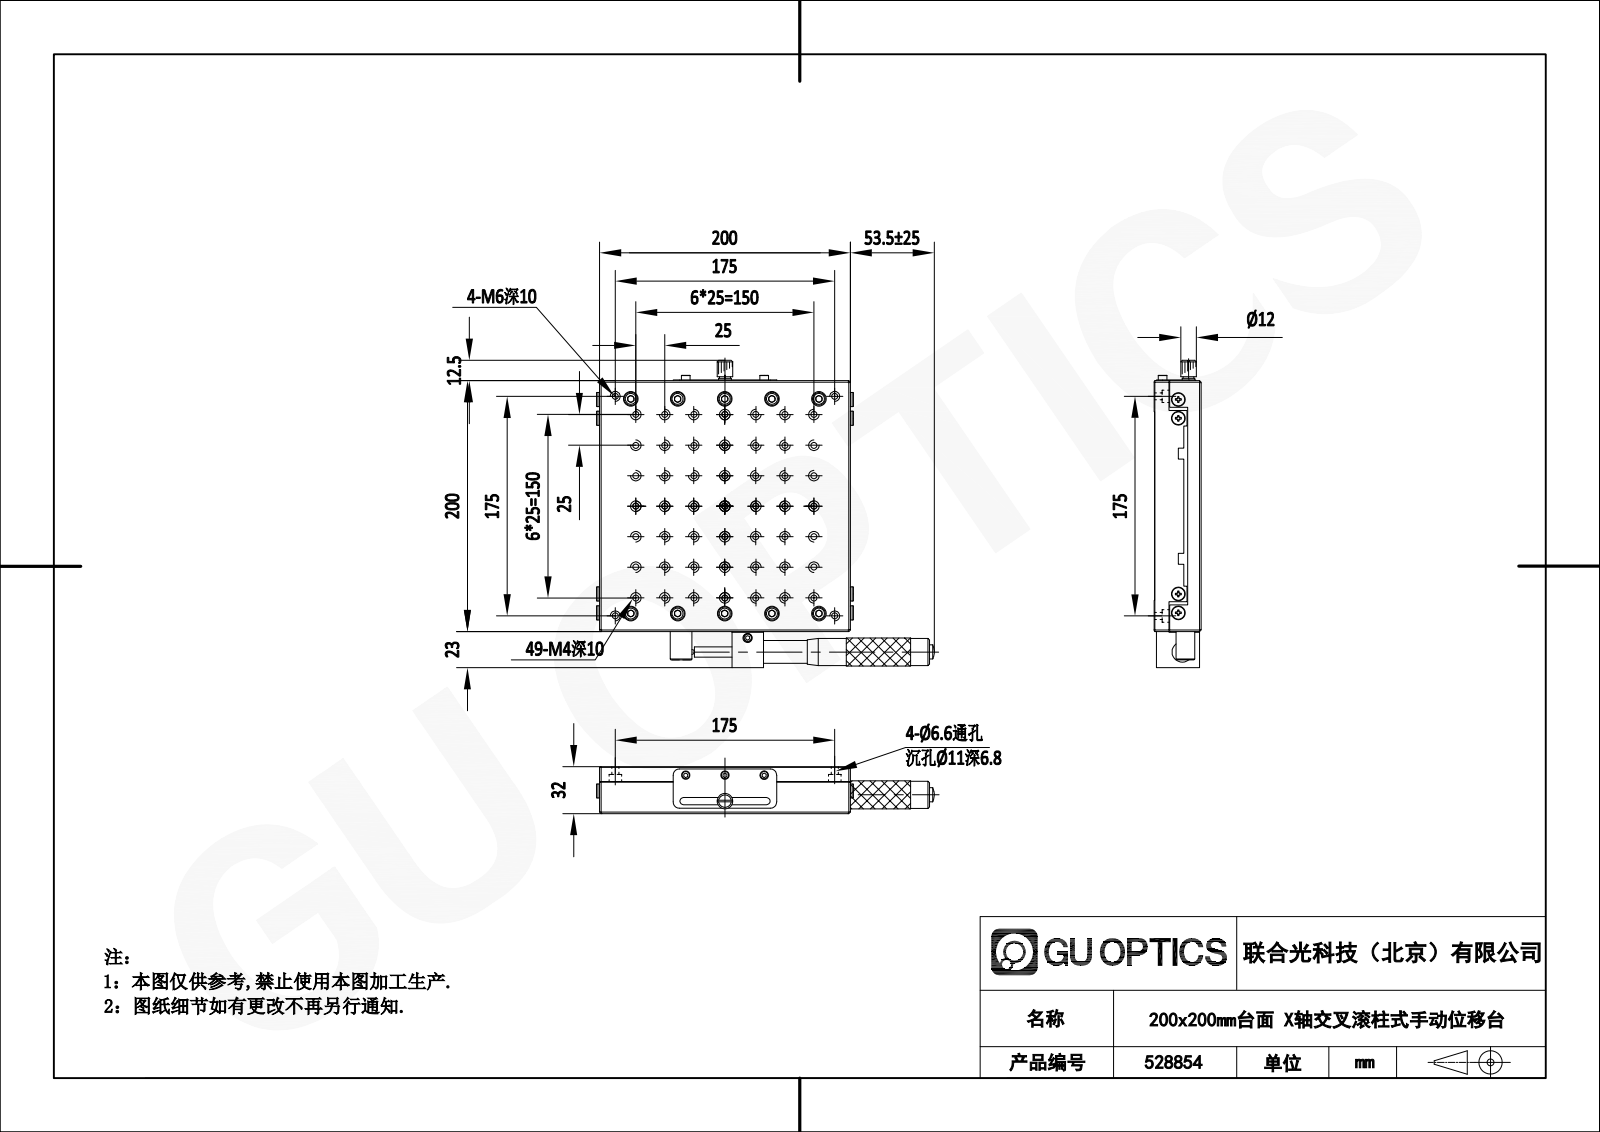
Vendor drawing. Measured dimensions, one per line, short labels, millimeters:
name: 528854
written by: SolidWorks 2020 (CONFIG_CONTROL_DESIGN)
unit: mm
bodies: 3 solids, 1746 faces (324 planar, 408 cylindrical, 1014 other)
size: 255.35 × 235.5 × 32
volume: 1 203 000 mm³; area: 224 847 mm²
holes: 49× ⌀3.24, 20× ⌀8.9, 4× ⌀4.92, 4× ⌀6.6, 4× ⌀11, 2× ⌀5.9, 2× ⌀7.3, 1× ⌀6, 1× ⌀6.5, 1× ⌀10
bosses: 20× ⌀8.5, 6× ⌀5.5, 5× ⌀9, 2× ⌀7, 1× ⌀18, 1× ⌀17.32, 1× ⌀17.3, 1× ⌀14.6
rounds: 6× R2.1, 1× R6
face distances: 10.5, 21.2, 31.7, 13, 2.5, 18.7, 9.5, 32, 11, 21.5
hole spacings: 40, 41.76, 158.14, 80, 80.89, 172.65, 12, 120.6
